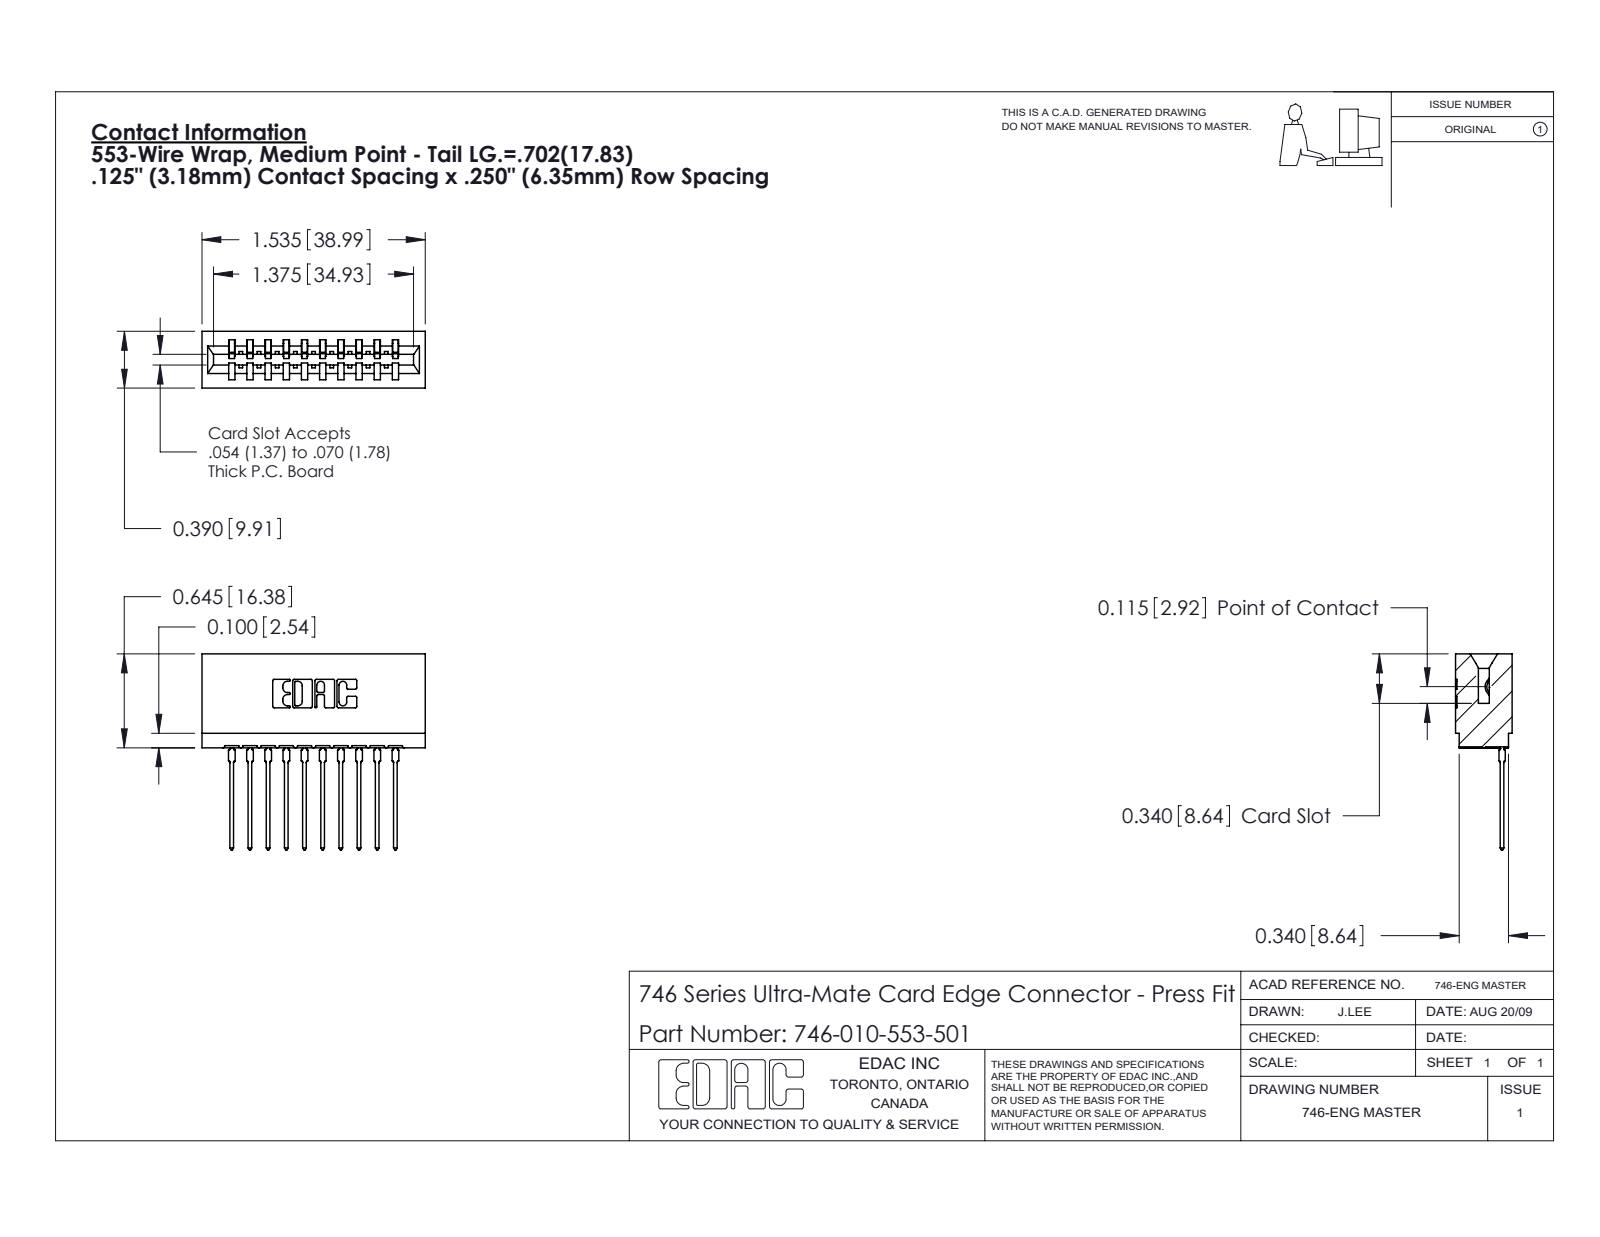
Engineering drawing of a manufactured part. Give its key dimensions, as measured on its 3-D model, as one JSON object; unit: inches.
{"part_name": "746 Part_.340 Slot Depth - 01; 746-292-001_553; 746-010-553-501", "step_written_by": "SolidWorks 2020 (CONFIG_CONTROL_DESIGN)", "units": "inches", "bodies": {"solids": 11, "faces": 1177, "planar": 685, "cylindrical": 232, "other": 260}, "overall_size": [1.535, 1.346, 0.39], "volume_in3": 0.281, "surface_area_in2": 9.174, "partial_cylinders_radius": [[0.01, 22], [0.021, 20], [0.015, 11], [0.007, 6], [0.031, 6], [0.005, 4], [0.011, 4], [0.026, 3]], "face_to_face_distances": [0.25, 0.5, 0.333, 0.057, 0.042, 0.125, 0.292, 0.375, 0.125, 0.39]}
